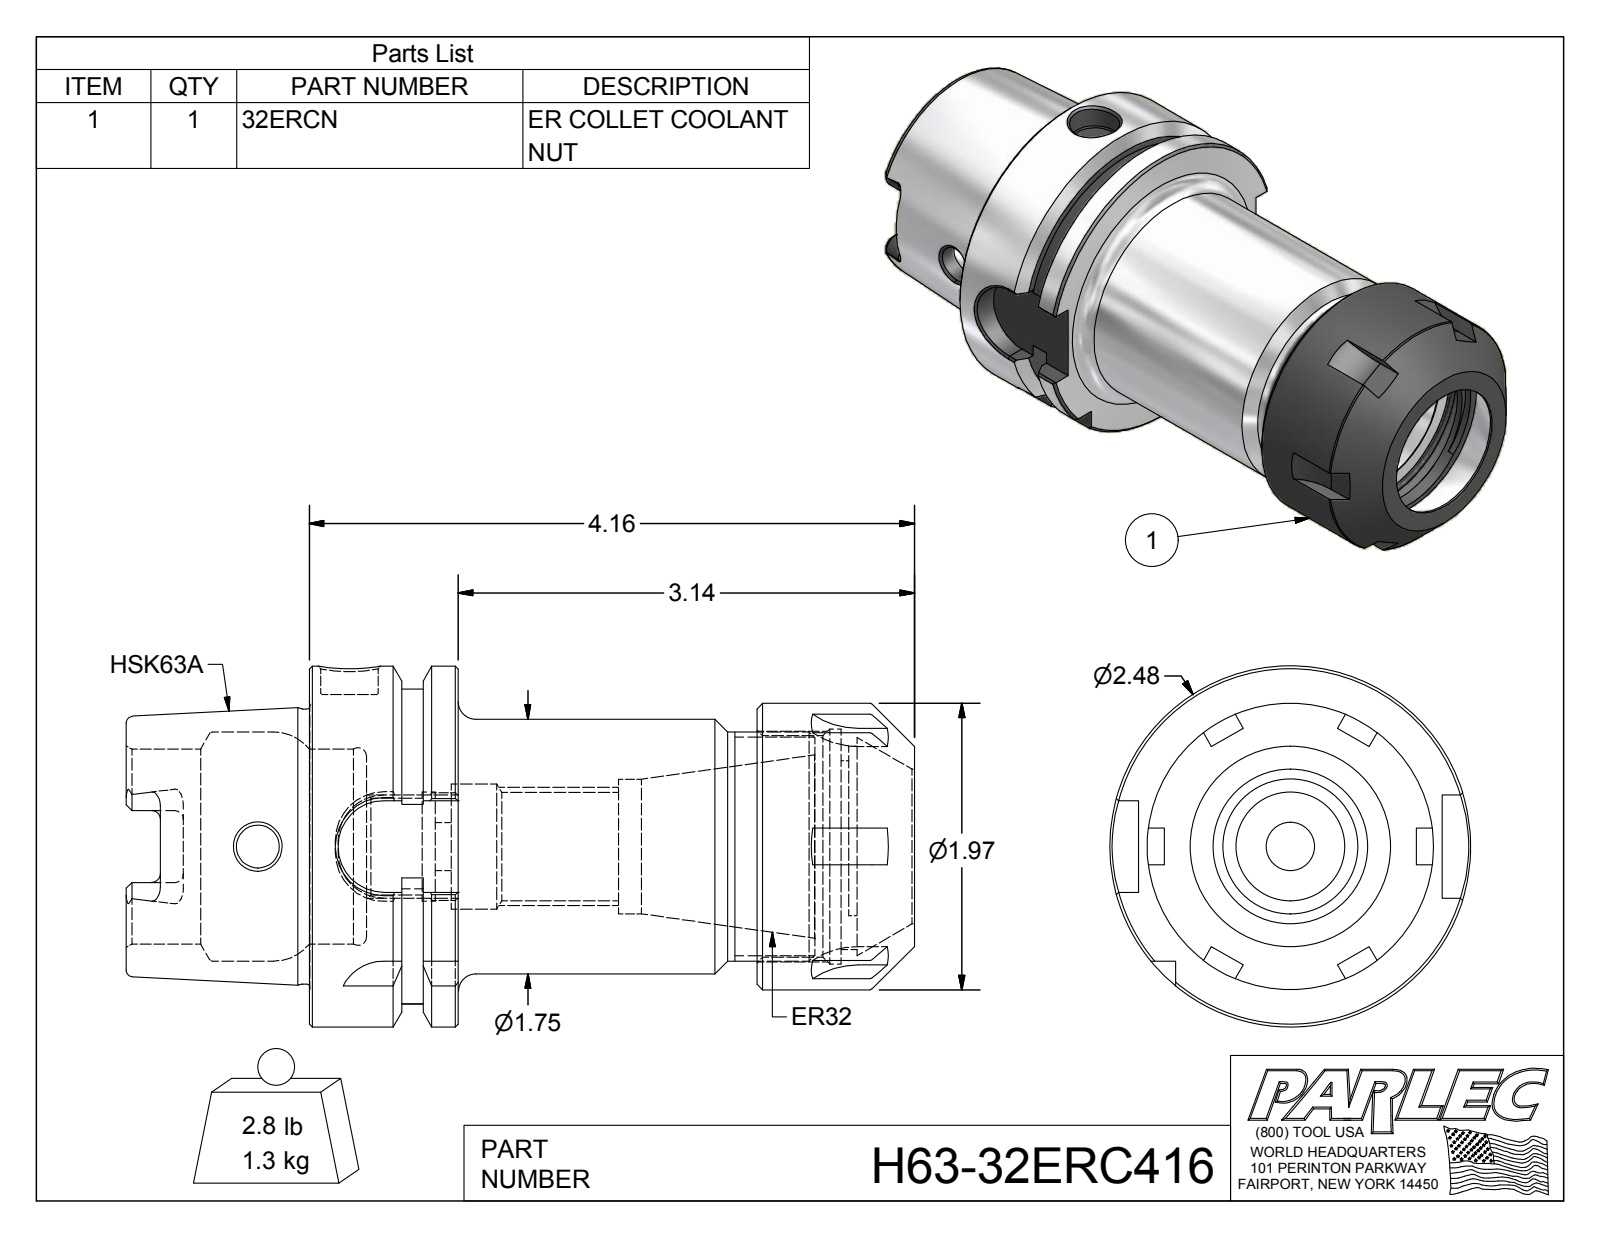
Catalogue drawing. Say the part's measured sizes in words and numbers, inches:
The part is named "H63-32ERC416; H63-32ER4-1; 32ERCN". Its 3-D file was written by "Autodesk Inventor 2012 (AUTOMOTIVE_DESIGN)". It is 2 solids with 186 faces: 76 planar, 49 cylindrical and 61 other. Overall it measures 5.42 by 2.48 by 2.48 inches. Its volume is 10.02 cubic inches and its surface area 69.74 square inches. Round holes: 1 of diameter 0.295, 1 of diameter 0.331, 1 of diameter 0.394, 1 of diameter 0.666, 1 of diameter 0.745, 1 of diameter 0.749, 1 of diameter 0.861, 1 of diameter 0.925, 1 of diameter 1.063, 1 of diameter 1.299, 1 of diameter 1.339, 1 of diameter 1.522. Round bosses or shafts: 1 of diameter 2.48, 1 of diameter 1.969, 1 of diameter 1.891, 1 of diameter 1.75. Partial cylindrical surfaces (rounded edges, fillets, slot ends): 6 of radius 0.059, 6 of radius 0.5, 4 of radius 0.113, 4 of radius 0.315, 1 of radius 0.689, 1 of radius 1.083. The main face-to-face distances are 1.024, 0.241, 0.389, 0.394, 0.63, 3.077, 2.683, 2.054, 3.656, 3.262. The hole center spacings are 0.059.
